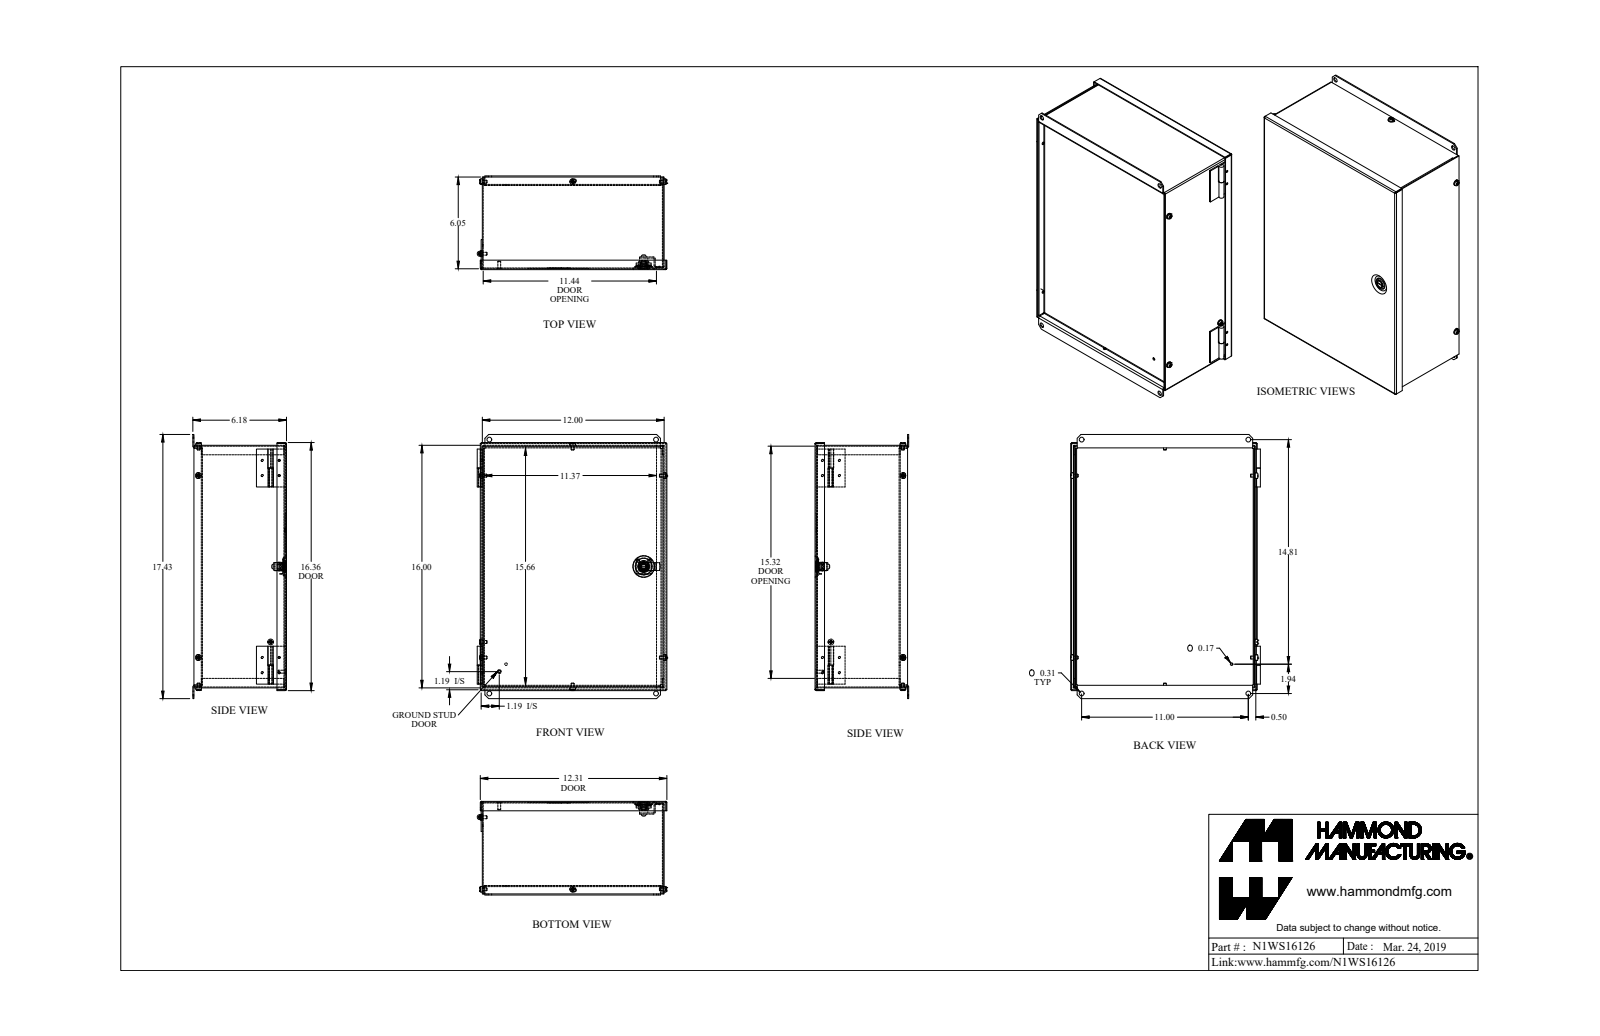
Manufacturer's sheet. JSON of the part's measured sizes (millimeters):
{"part_name": "N1WS16126", "step_written_by": "SolidWorks 2018 (AUTOMOTIVE_DESIGN)", "units": "millimeters", "bodies": {"solids": 17, "faces": 607, "planar": 328, "cylindrical": 214, "other": 65}, "overall_size": [442.6, 318, 156.9], "volume_mm3": 836900, "surface_area_mm2": 1080000, "round_holes": [[3.6, 8], [4.3, 5], [7.9, 4], [4.7, 1], [8.1, 1], [12.1, 1]], "round_bosses_or_shafts": [[3.3, 8], [9.5, 4], [4.8, 4], [20, 1], [13.9, 1], [12, 1], [11.9, 1], [9.3, 1]], "partial_cylinders_radius": [[0.7, 9], [2.2, 9], [0.9, 8], [2.7, 6], [2.8, 6], [0.3, 4], [2.5, 4], [2, 2]], "face_to_face_distances": [1.4, 1.8, 1.4, 303.4, 141.3, 142.8, 139.5, 140.9, 405, 301.9], "hole_center_spacings": [25.4, 28.4, 38.1, 330.2, 331.4, 304.8, 106.6, 109.6]}
